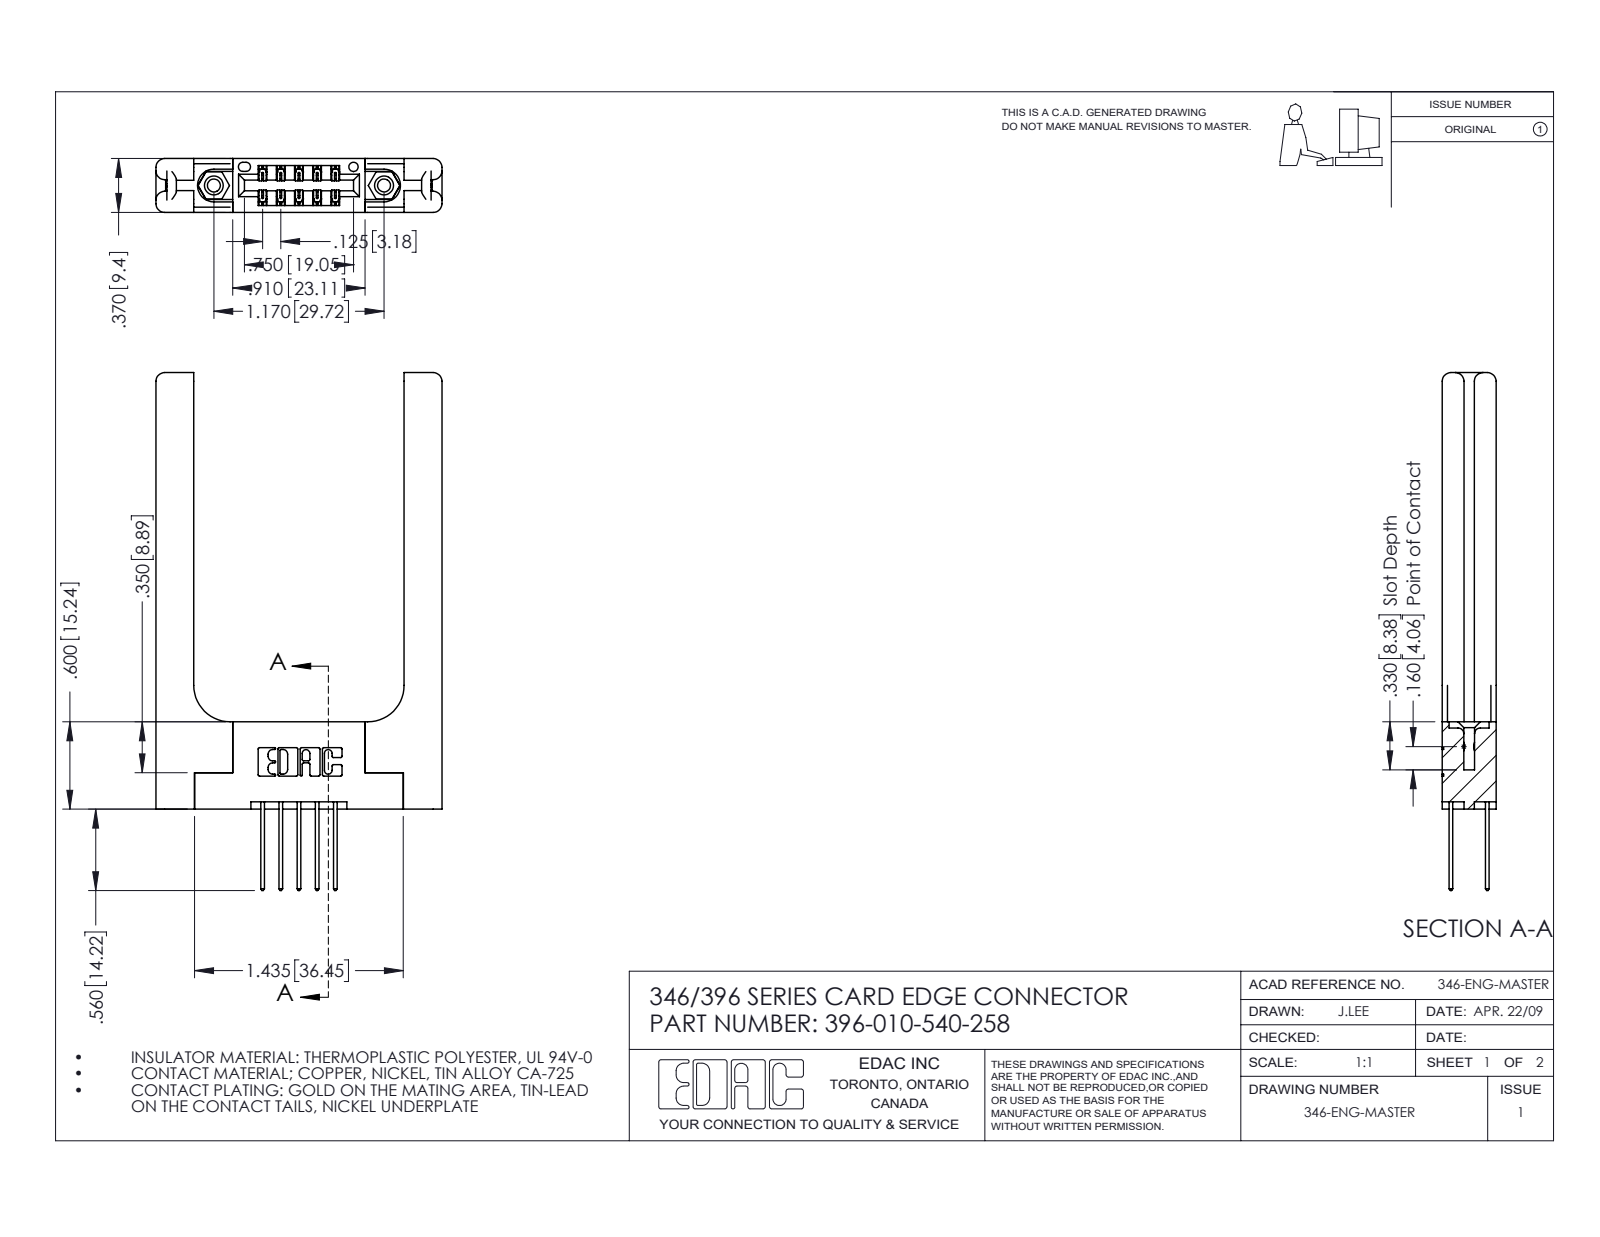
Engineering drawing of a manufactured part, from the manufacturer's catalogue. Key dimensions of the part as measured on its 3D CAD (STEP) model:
Part name (STEP PRODUCT): 346-220-058_345-220-058; 345-250-001_345-250-001-102; 396-010-540-258; 346 Part_Flush Mounting Lugs - 0.156 Dia-TH (+1 more)
STEP written by: SolidWorks 2016 (CONFIG_CONTROL_DESIGN)
Units: inches
Bodies: 15 solids, 898 faces (574 planar, 264 cylindrical, 60 other)
Overall size (bounding box): 3.56 × 1.966 × 0.37
Volume: 0.739 in³ · Surface area: 16.93 in²
Round holes (diameter × count): ⌀0.089 ×2, ⌀0.125 ×2, ⌀0.156 ×2, ⌀0.064 ×1
Round bosses / shafts (diameter × count): ⌀0.155 ×2
Partial cylindrical surfaces — rounded edges, fillets, slot ends (radius × count): R0.01 ×22, R0.06 ×16, R0.006 ×15, R0.01 ×10, R0.007 ×6, R0.031 ×6, R0.026 ×3, R0.014 ×2
Main face-to-face distances: 0.37, 0.15, 0.22, 0.25, 0.072, 0.148, 1.446, 0.102, 0.048, 0.322
Hole centre spacings: 0.246, 0.969, 1.17
